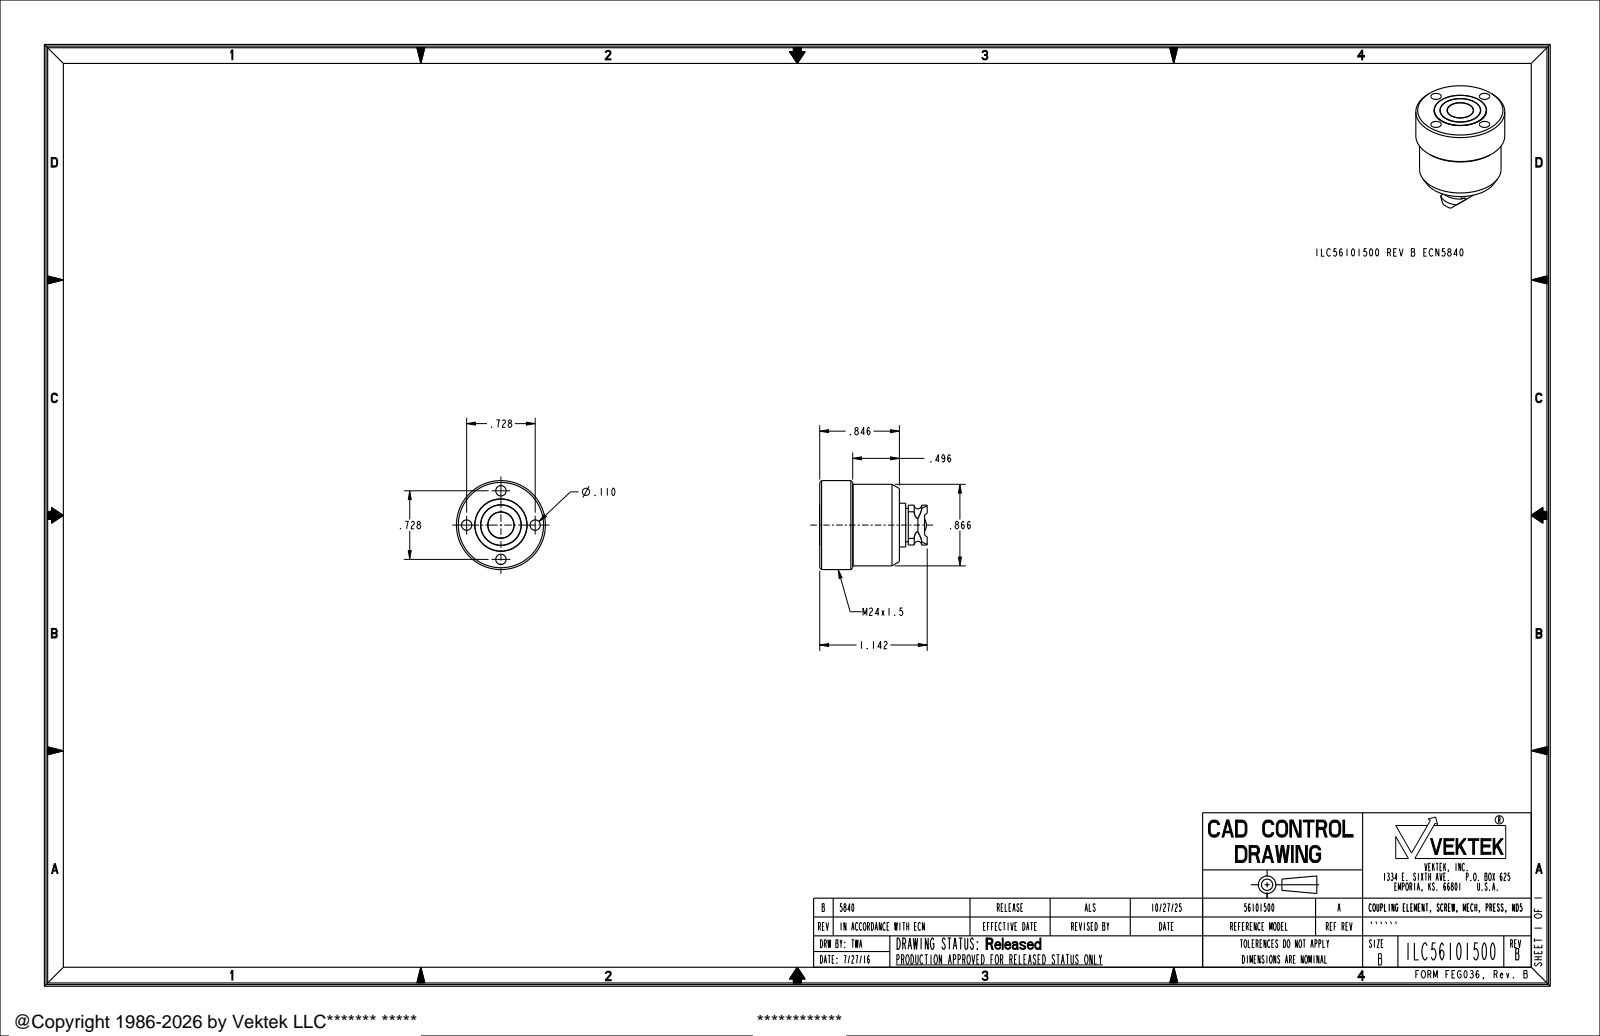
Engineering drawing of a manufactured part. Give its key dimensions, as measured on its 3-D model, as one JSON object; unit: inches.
{"part_name": "ILC56101500", "step_written_by": "PRO/ENGINEER BY PARAMETRIC TECHNOLOGY CORPORATION, 2013320 (CONFIG_CONTROL_DESIGN)", "units": "inches", "bodies": {"solids": 0, "faces": 72, "planar": 19, "cylindrical": 29, "other": 24}, "overall_size": [1.143, 0.945, 0.945], "round_holes": [[0.11, 4]], "round_bosses_or_shafts": [[0.945, 1], [0.87, 1], [0.866, 1], [0.551, 1], [0.465, 1], [0.354, 1]], "partial_cylinders_radius": [[0.138, 1], [0.212, 1]], "face_to_face_distances": [0.846, 0.848, 0.915, 0.913, 0.067, 0.201, 0.352, 0.35, 0.496, 0.563], "hole_center_spacings": [0.515, 0.728]}
